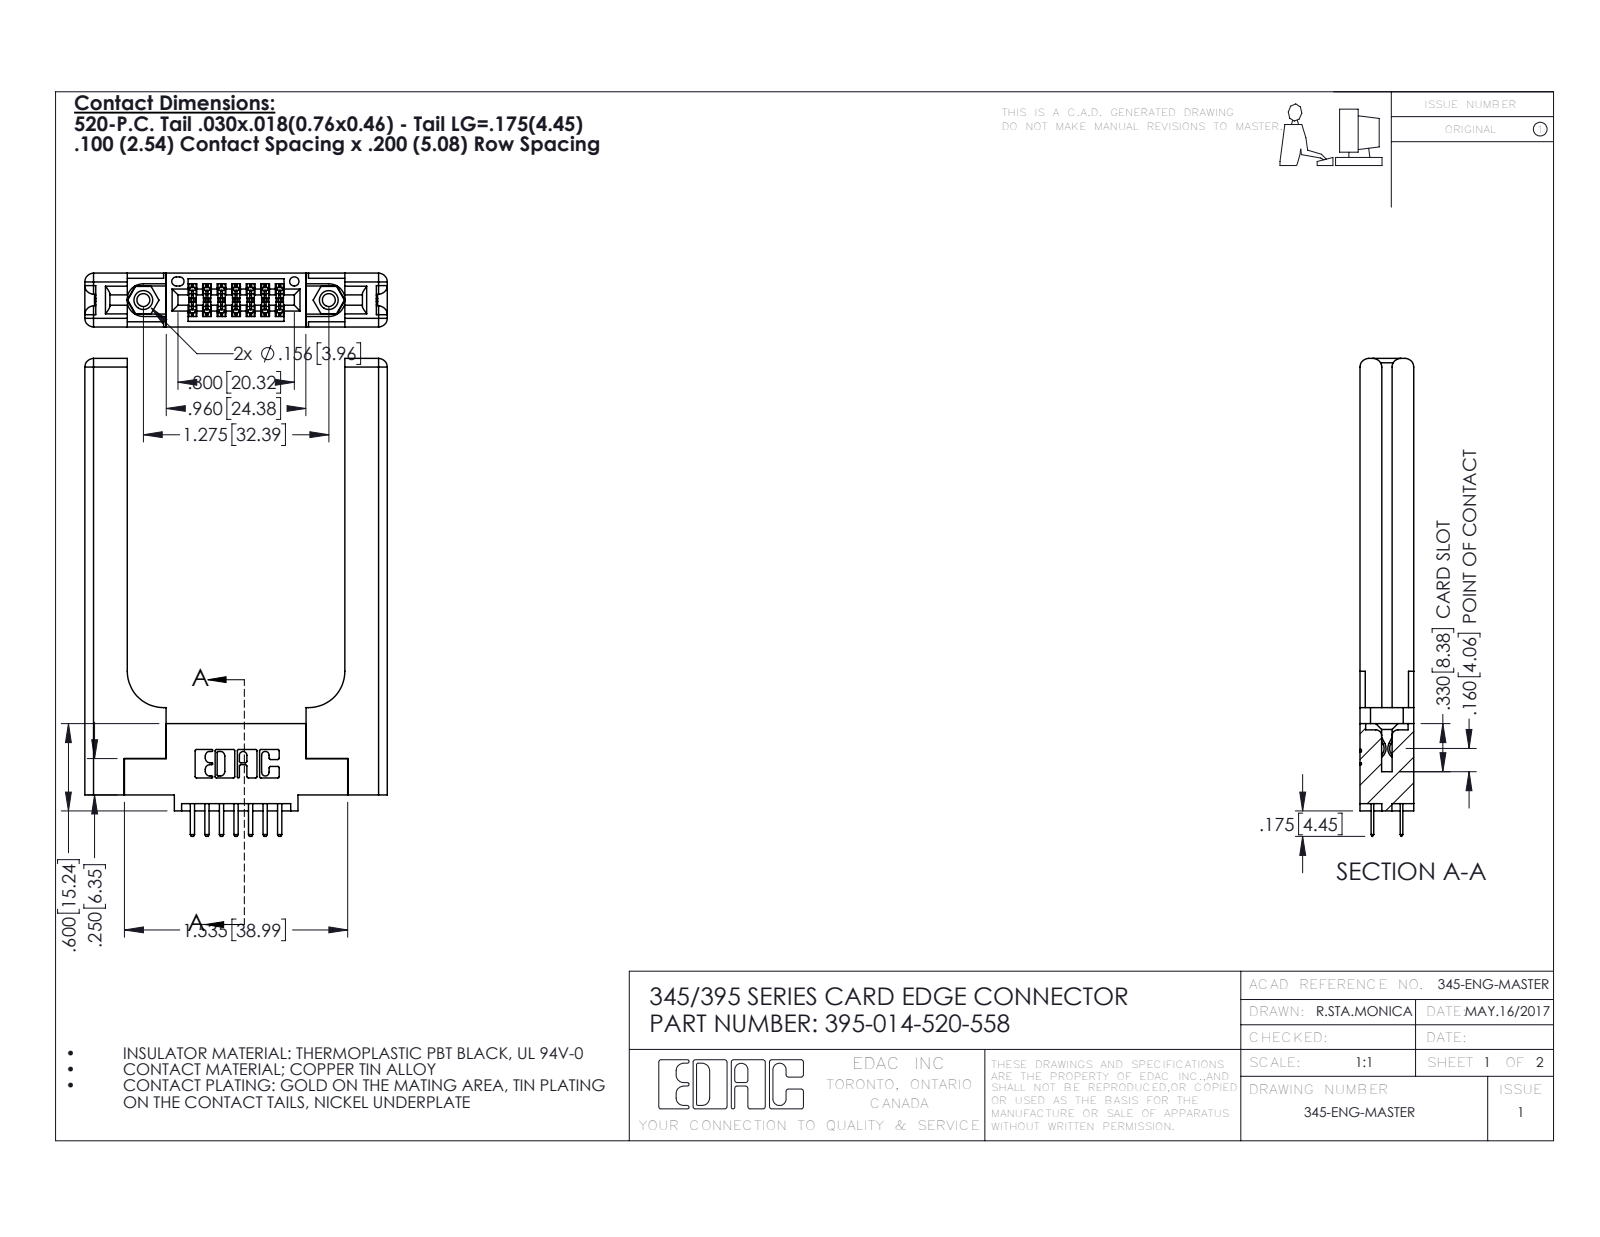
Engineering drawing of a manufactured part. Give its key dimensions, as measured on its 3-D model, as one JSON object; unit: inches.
{"part_name": "345 Part_0.110 Offset - 0.156 Dia-TH; 395-014-520-558; 345-220-058_345-220-058; 345-292-001_345-293-120 (+1 more)", "step_written_by": "SolidWorks 2016 (CONFIG_CONTROL_DESIGN)", "units": "inches", "bodies": {"solids": 19, "faces": 1142, "planar": 722, "cylindrical": 360, "other": 60}, "overall_size": [3.285, 2.079, 0.37], "volume_in3": 0.806, "surface_area_in2": 17.74, "round_holes": [[0.089, 2], [0.125, 2], [0.156, 2], [0.064, 1]], "round_bosses_or_shafts": [[0.155, 2]], "partial_cylinders_radius": [[0.01, 22], [0.006, 21], [0.01, 18], [0.06, 16], [0.007, 6], [0.031, 6], [0.026, 3], [0.014, 2]], "face_to_face_distances": [0.37, 0.15, 0.22, 0.072, 0.298, 0.077, 0.148, 1.496, 0.071, 0.292], "hole_center_spacings": [0.27, 1.045, 1.275]}
